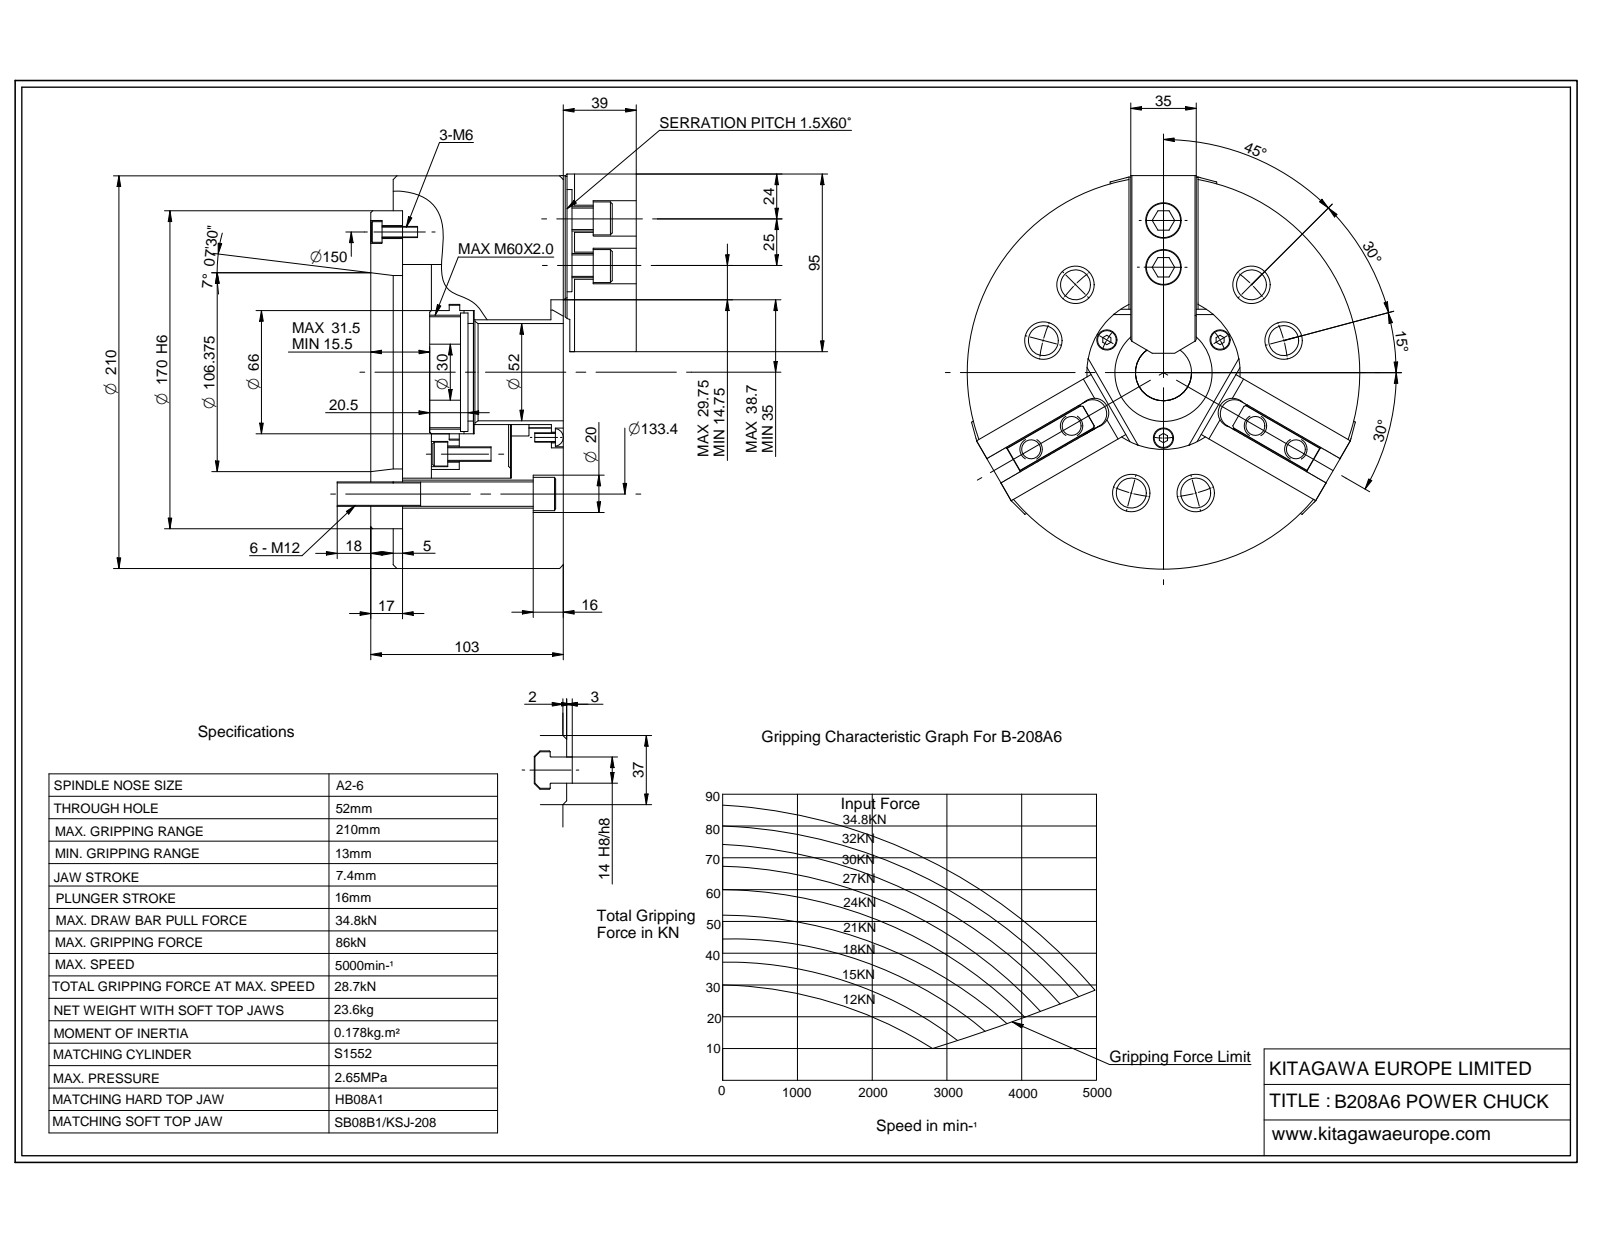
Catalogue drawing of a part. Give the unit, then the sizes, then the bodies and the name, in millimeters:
Units: millimetres
Overall size (bounding box): 210 × 210 × 105
Round holes (diameter × count): ⌀13.5 ×12, ⌀3 ×6, ⌀6.8 ×6, ⌀9 ×6, ⌀14 ×6, ⌀20 ×6, ⌀11 ×5, ⌀4 ×4, ⌀4.2 ×3, ⌀5 ×3, ⌀5.5 ×3, ⌀6.6 ×3
Round bosses / shafts (diameter × count): ⌀210 ×1, ⌀105.5 ×1, ⌀72 ×1, ⌀64.8 ×1
Partial cylindrical surfaces — rounded edges, fillets, slot ends (radius × count): R0.4 ×12, R0.8 ×12, R0.6 ×6, R5.03 ×6, R5.5 ×6, R7.5 ×6, R4 ×3, R5 ×3
Main face-to-face distances: 12, 103, 91, 25.5, 17, 1, 5, 86, 13.5, 77.5
Hole centre spacings: 20.25, 34.23, 57.24, 96.44, 96.71, 96.74, 112.51, 112.53
Volume: 2 680 000 mm³ · Surface area: 292 825 mm²
Bodies: 1 solid, 1216 faces (862 planar, 197 cylindrical, 157 other)
Part name (STEP PRODUCT): B208A06
STEP written by: ST-DEVELOPER v16.7 (AUTOMOTIVE_DESIGN)
